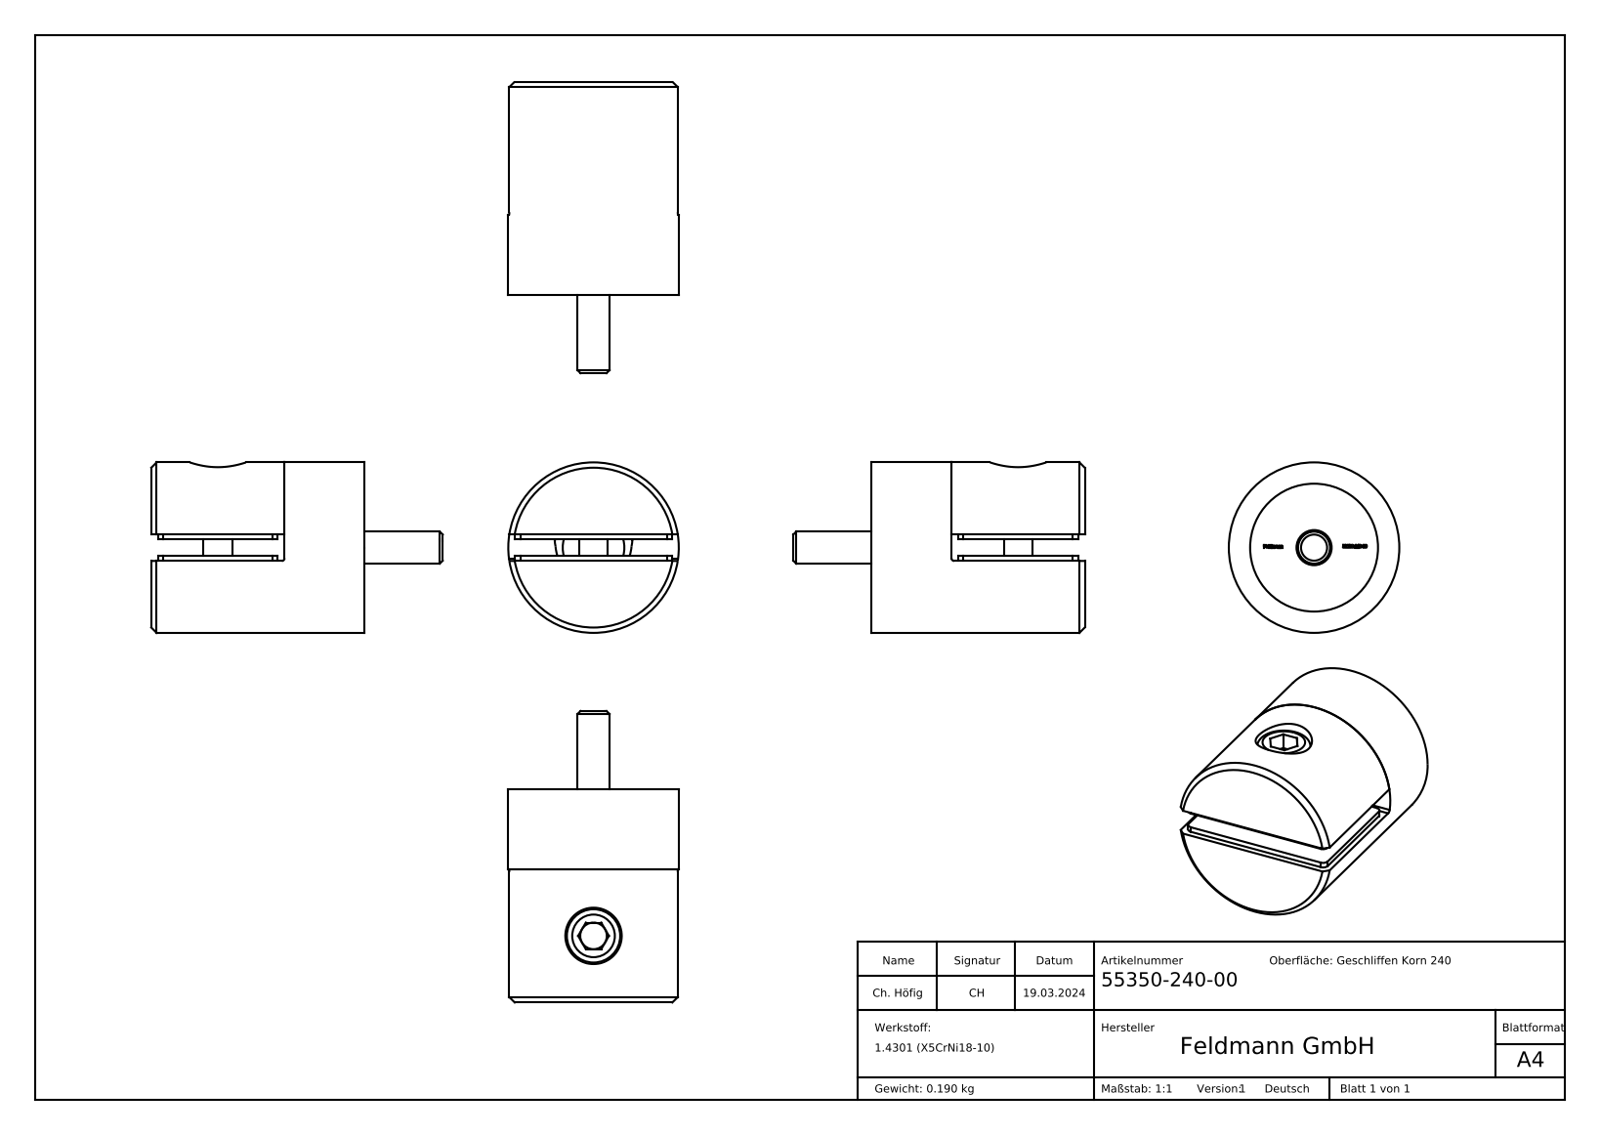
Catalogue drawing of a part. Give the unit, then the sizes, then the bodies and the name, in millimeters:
Units: millimetres
Overall size (bounding box): 54.7 × 32 × 32
Round holes (diameter × count): ⌀4 ×4, ⌀5 ×1, ⌀6.5 ×1, ⌀6.6 ×1, ⌀7 ×1, ⌀10.58 ×1, ⌀24 ×1
Round bosses / shafts (diameter × count): ⌀4 ×2, ⌀32 ×1, ⌀11.57 ×1, ⌀10 ×1, ⌀6 ×1, ⌀5.35 ×1
Partial cylindrical surfaces — rounded edges, fillets, slot ends (radius × count): R1 ×4, R0.5 ×1, R7.15 ×1, R7.3 ×1
Main face-to-face distances: 4, 1, 5, 3, 25, 9.5, 34.5, 15, 5.5, 40
Hole centre spacings: 10.31, 10.47, 13.25, 13, 13.5
Volume: 25 948 mm³ · Surface area: 13 185 mm²
Bodies: 6 solids, 366 faces (190 planar, 33 cylindrical, 143 other)
Part name (STEP PRODUCT): socket countersunk head screw_din; 5533X-240 Teil2_55350-240-XX Teil2; DIN 912 M6x18; 5533X-240 Teil2 (+7 more)
STEP written by: SolidWorks 2018 (CONFIG_CONTROL_DESIGN)
